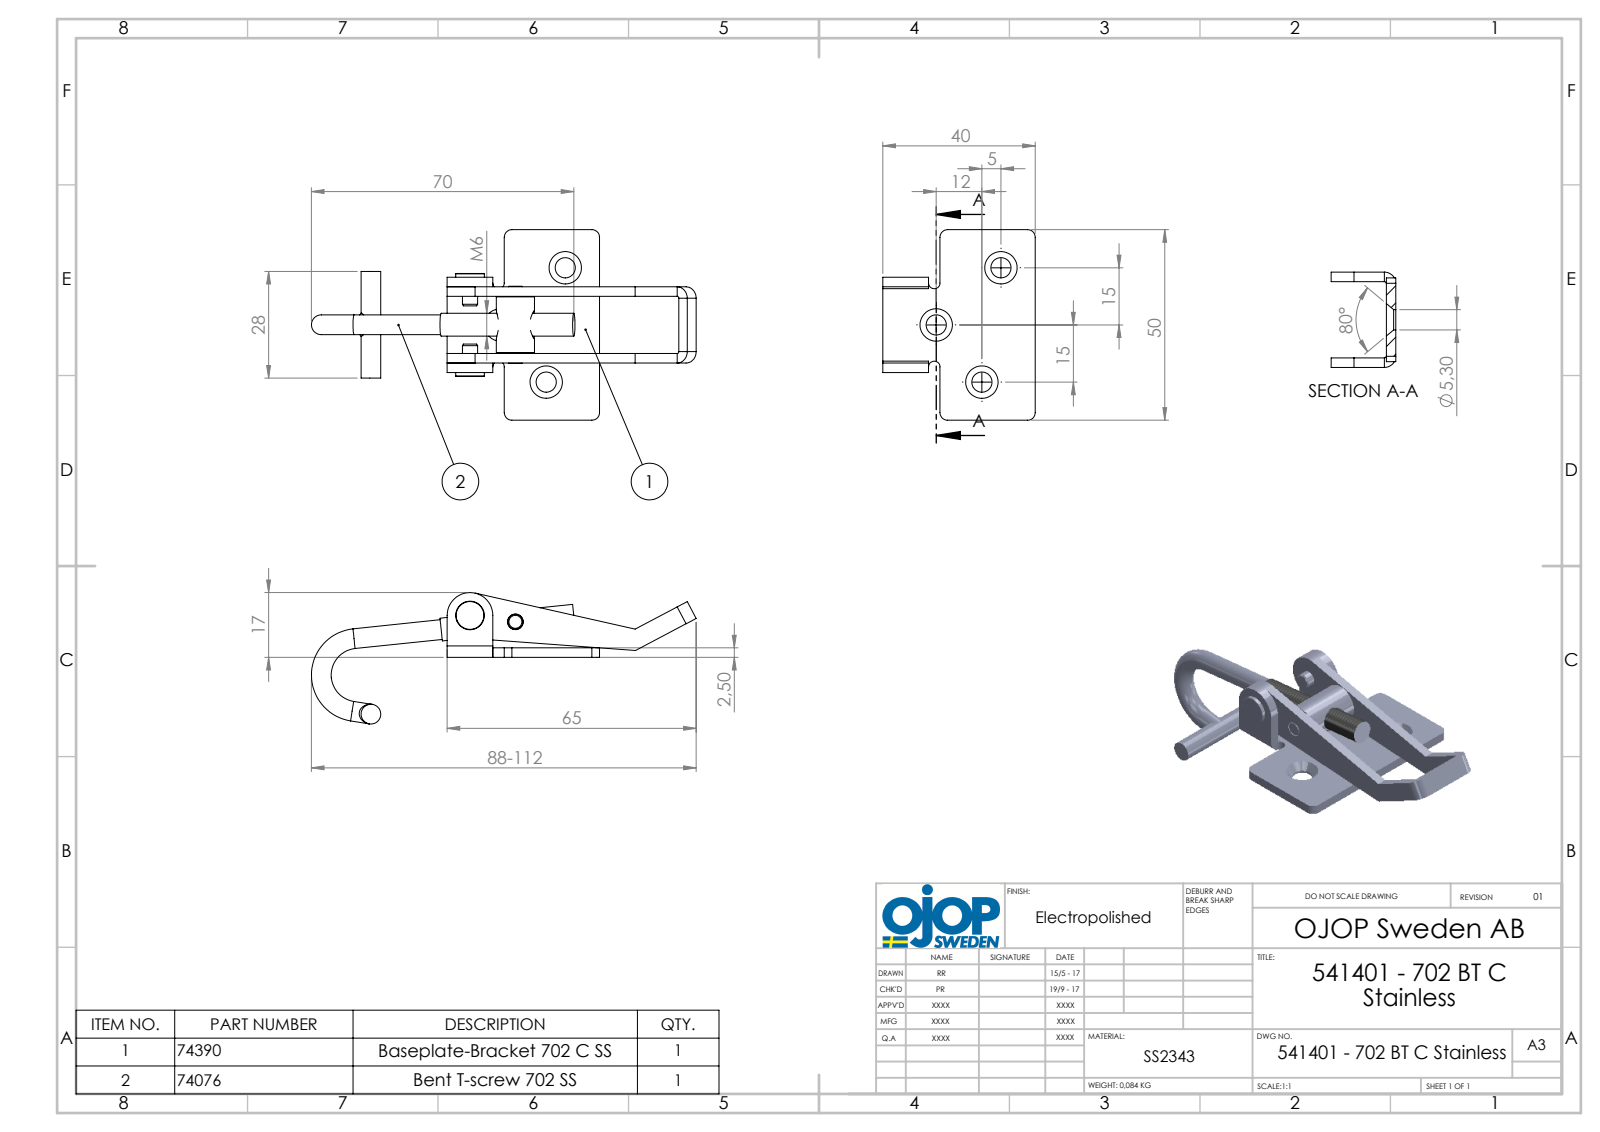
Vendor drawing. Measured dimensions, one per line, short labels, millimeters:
name: 702 - Rulle; 541401 - 702 BT C Stainless; 702 - Bygel; 702 - Böjd T-skruv M6 (+2 more)
written by: SolidWorks 2015 (AUTOMOTIVE_DESIGN)
unit: mm
bodies: 6 solids, 149 faces (58 planar, 65 cylindrical, 26 other)
size: 109.99 × 50 × 25.73
volume: 11 107 mm³; area: 10 617 mm²
holes: 3× ⌀5.3, 2× ⌀4.1, 1× ⌀5, 1× ⌀6
bosses: 3× ⌀5.18, 2× ⌀4, 1× ⌀10, 1× ⌀7.5, 1× ⌀6
rounds: 4× R0.5, 4× R2, 4× R3, 2× R1.5, 1× R6
face distances: 2.5, 17.5, 20, 15, 5, 22.5, 25, 12.5, 32.5, 35
hole spacings: 12.03, 19.21, 22.67, 30.41
